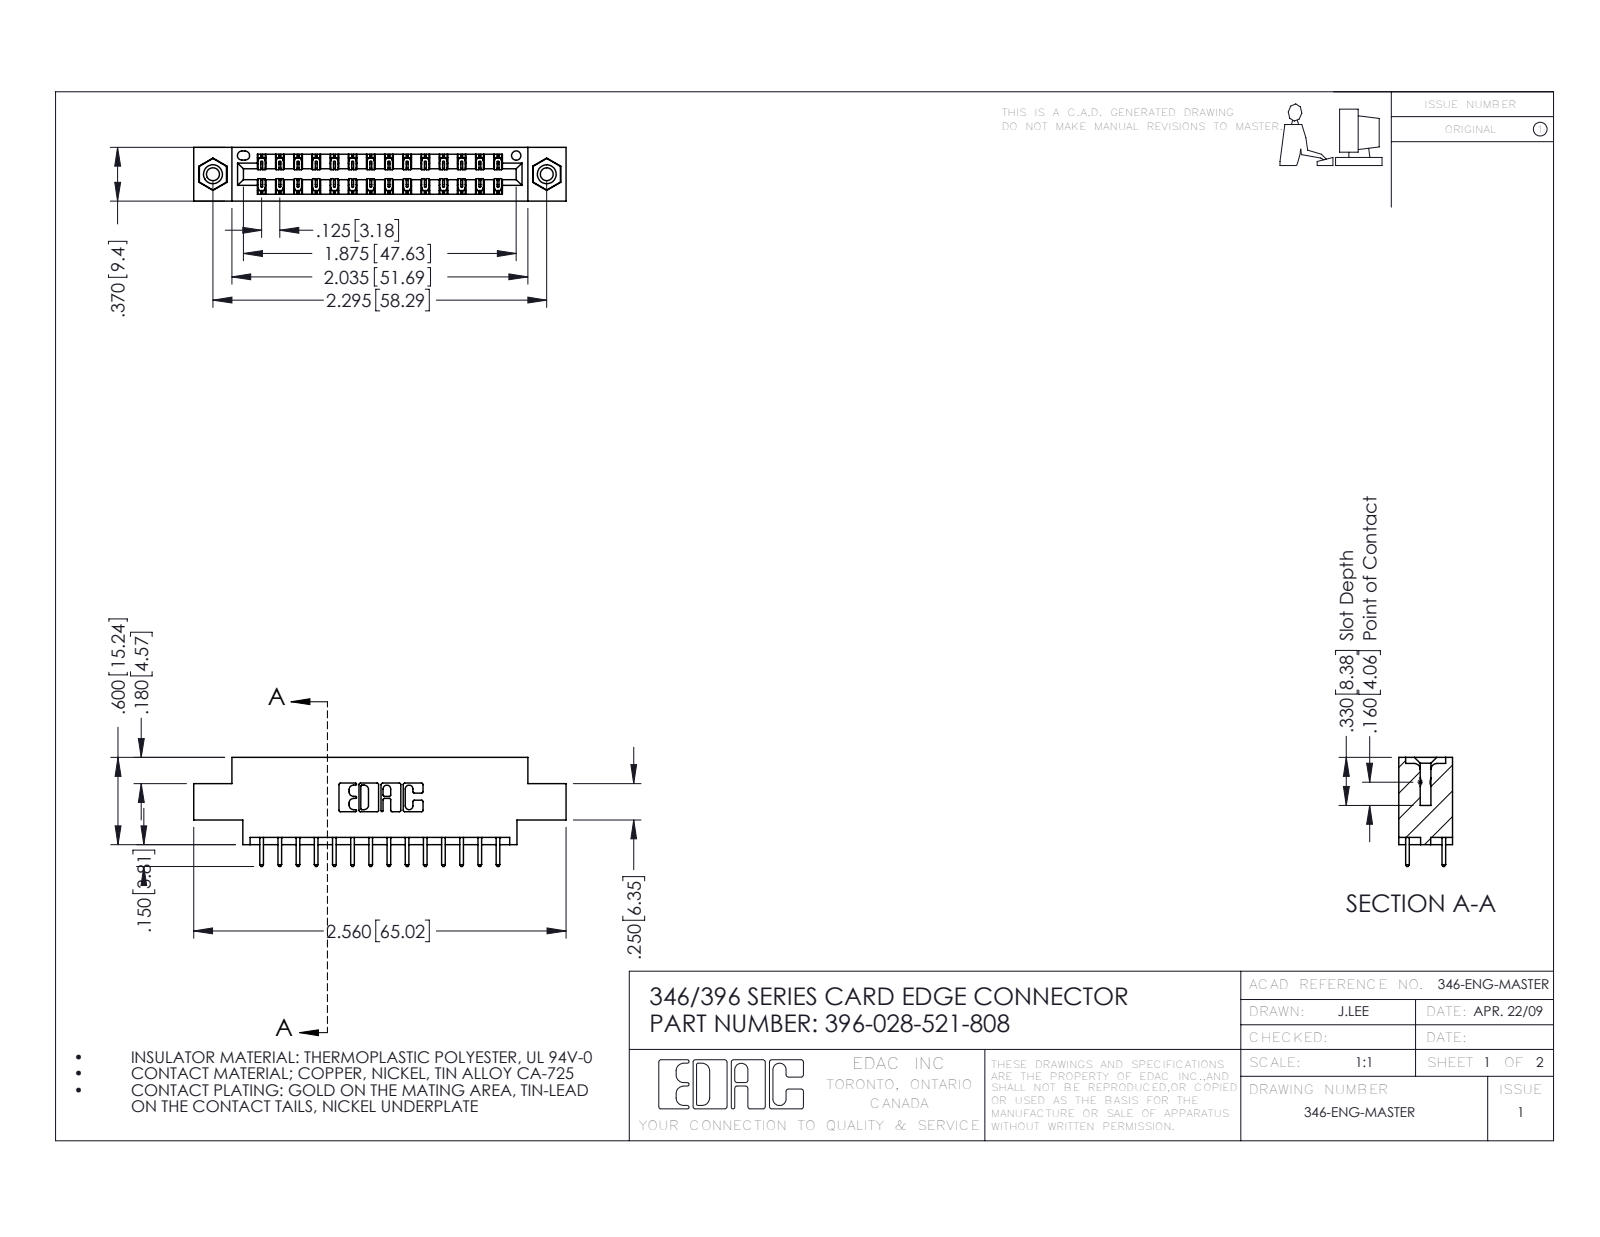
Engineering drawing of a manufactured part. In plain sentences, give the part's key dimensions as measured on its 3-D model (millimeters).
The part is named "346 Part_0.170 Offset - 0.156 Dia-TI; 345-292-001_345-293-121; 345-250-001_345-250-003-102; 396-028-521-808". Its 3-D file was written by "SolidWorks 2016 (CONFIG_CONTROL_DESIGN)". It is 31 solids with 1642 faces: 1092 planar, 534 cylindrical and 16 other. Overall it measures 65 by 19.1 by 9.4 millimeters. Its volume is 5 950 cubic millimeters and its surface area 7 865 square millimeters. Round holes: 2 of diameter 2.3, 2 of diameter 3.2, 2 of diameter 4, 1 of diameter 1.6. Round bosses or shafts: 2 of diameter 3.9. Partial cylindrical surfaces (rounded edges, fillets, slot ends): 42 of radius 0.2, 28 of radius 0.3, 22 of radius 0.3, 6 of radius 0.2, 6 of radius 0.8, 3 of radius 0.7, 2 of radius 0.4, 2 of radius 0.6. The main face-to-face distances are 1.2, 8.2, 9.4, 6.4, 1.8, 7.6, 0.6, 7, 5.6, 3.8. The hole center spacings are 6.2, 53.1, 58.3.
